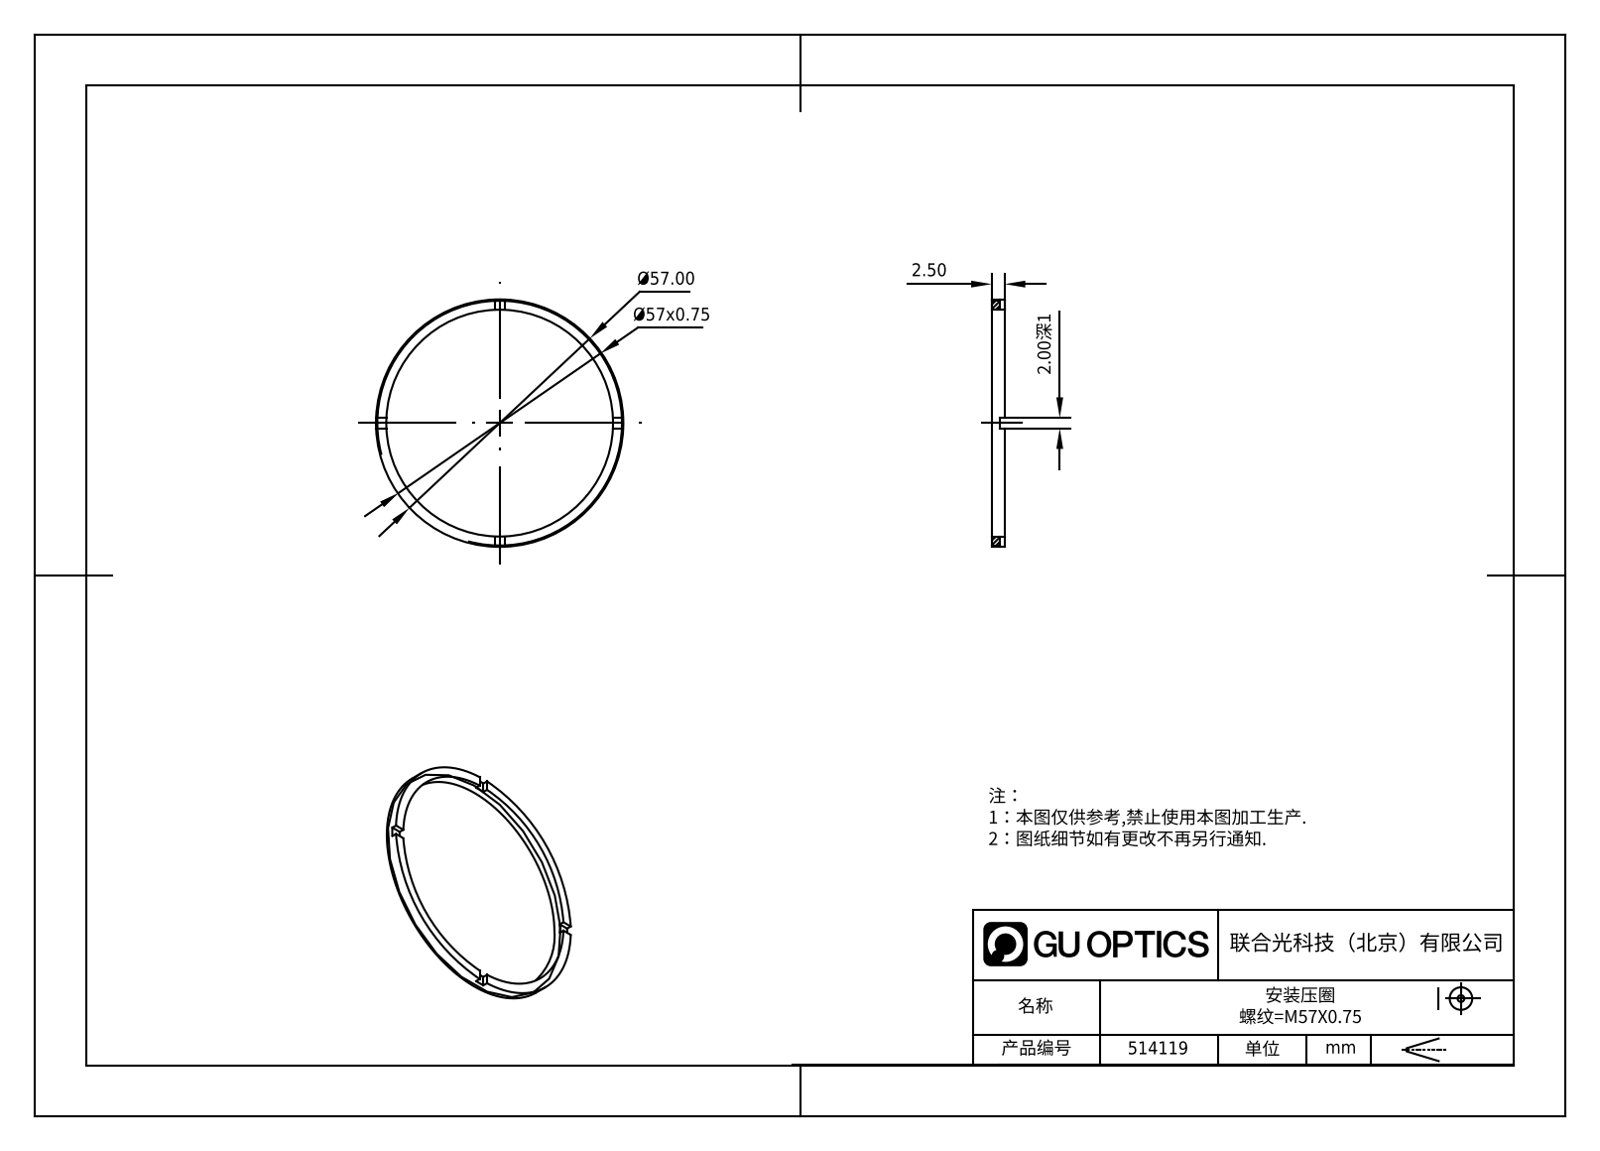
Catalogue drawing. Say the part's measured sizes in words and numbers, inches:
The part is named "514119". Its 3-D file was written by "SolidWorks 2020 (CONFIG_CONTROL_DESIGN)". It is 1 solid with 21 faces: 17 planar, 4 cylindrical and 0 other. Overall it measures 2.244 by 2.244 by 0.098 inches. Its volume is 0.064 cubic inches and its surface area 2.66 square inches. Round holes: 1 of diameter 2.047. Round bosses or shafts: 1 of diameter 2.244. The main face-to-face distances are 0.098, 0.059, 0.039, 0.079.
